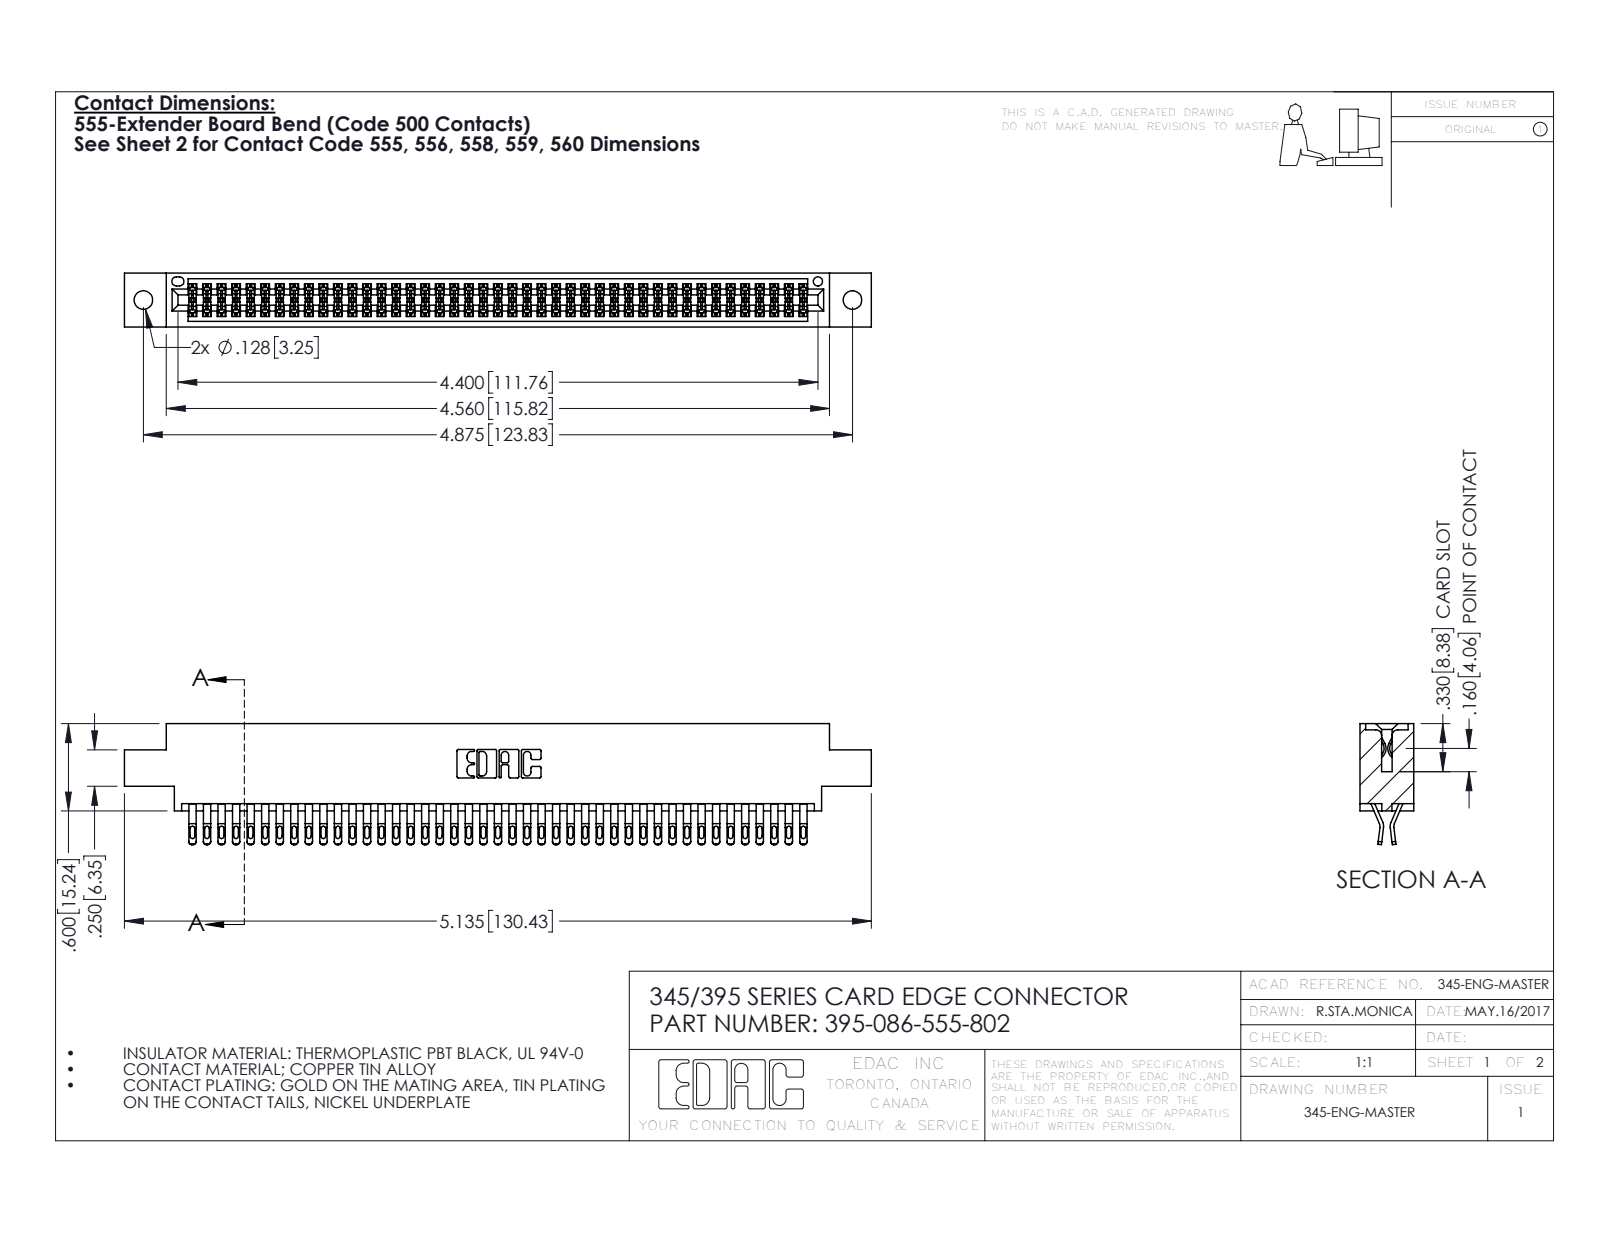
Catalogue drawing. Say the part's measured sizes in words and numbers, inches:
The part is named "395-086-555-802; 345-292-001_555 Tail; 345 Part_0.170 Offset - 0.128 Dia". Its 3-D file was written by "SolidWorks 2016 (CONFIG_CONTROL_DESIGN)". It is 87 solids with 4946 faces: 2750 planar, 2196 cylindrical and 0 other. Overall it measures 5.135 by 0.832 by 0.37 inches. Its volume is 0.78 cubic inches and its surface area 30.45 square inches. Round holes: 2 of diameter 0.128, 1 of diameter 0.064. Partial cylindrical surfaces (rounded edges, fillets, slot ends): 215 of radius 0.016, 172 of radius 0.02, 129 of radius 0.006, 22 of radius 0.01, 6 of radius 0.007, 6 of radius 0.031, 3 of radius 0.026, 2 of radius 0.01. The main face-to-face distances are 0.298, 0.072, 0.37, 0.025, 0.2, 0.098, 0.272, 0.225, 0.175, 0.149. The hole center spacings are 0.27, 4.639, 4.875.
